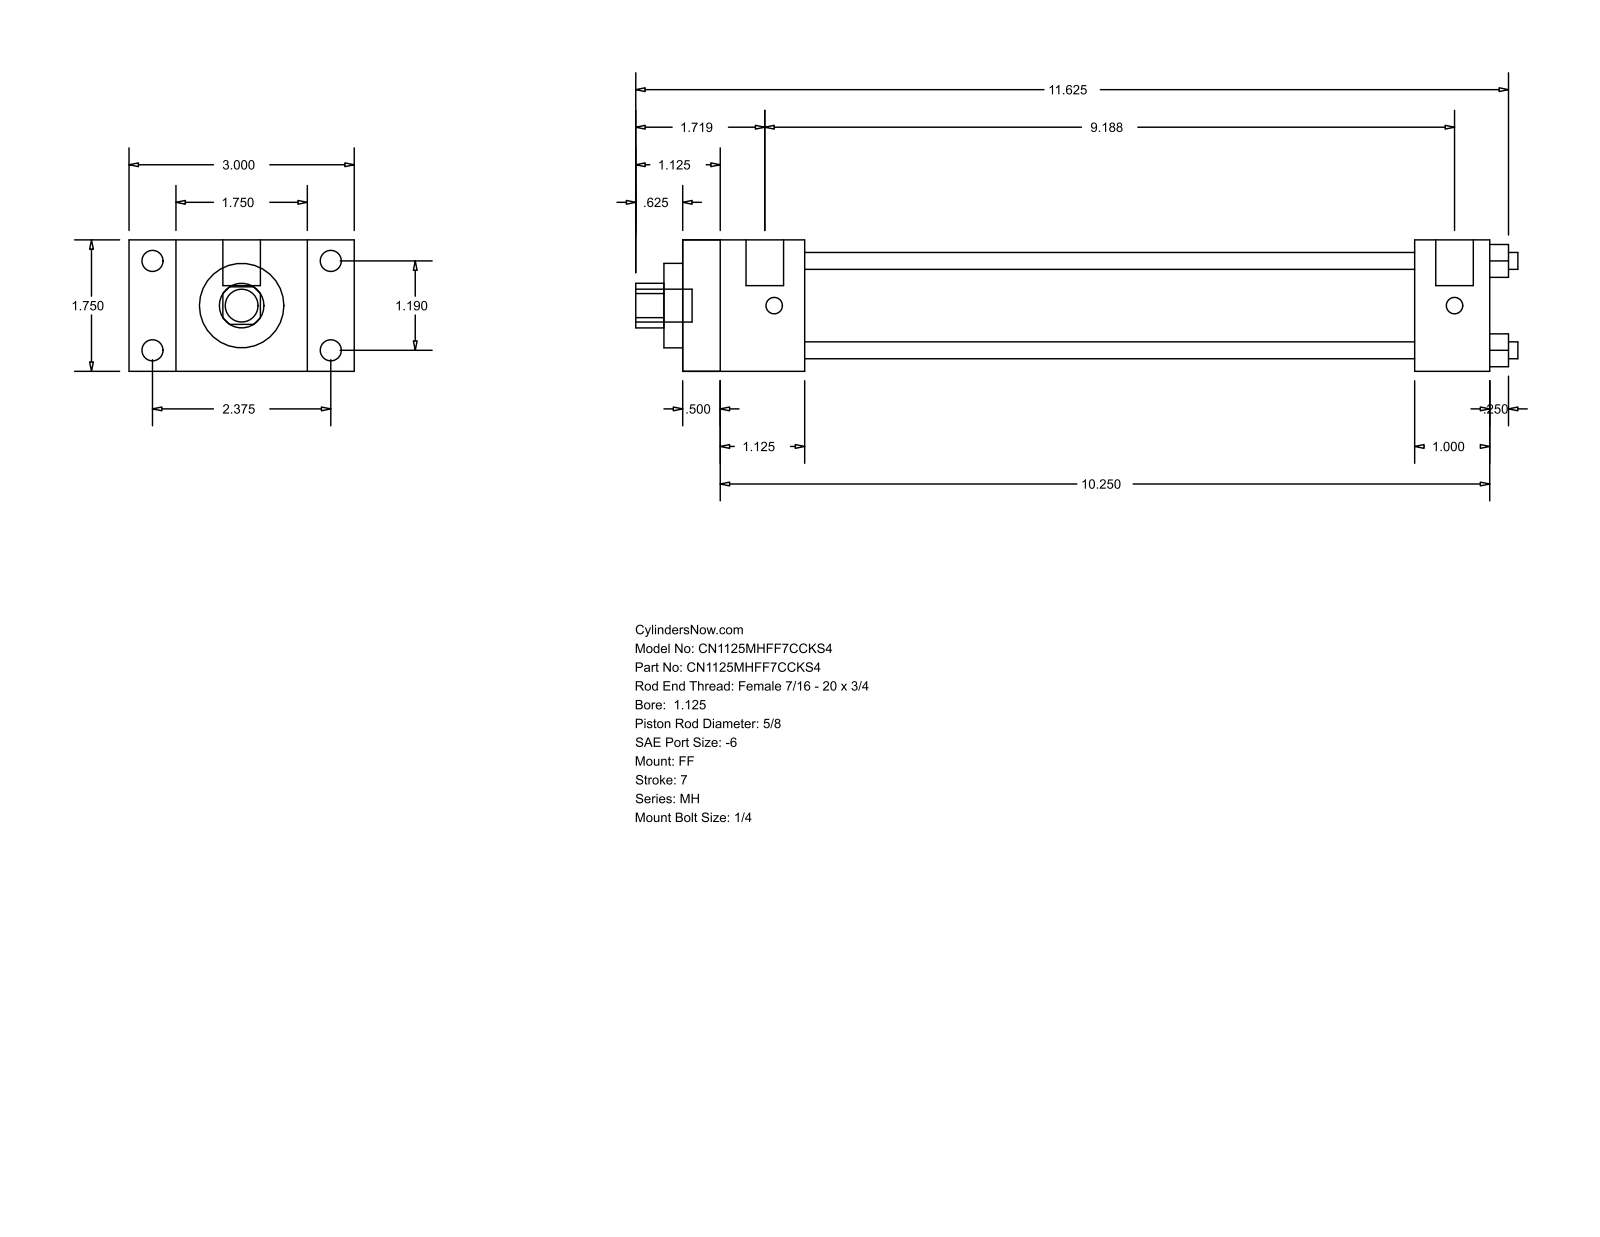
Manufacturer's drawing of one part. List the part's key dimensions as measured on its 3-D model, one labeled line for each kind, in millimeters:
Part name (STEP PRODUCT): MH_FF__0112_0.625
STEP written by: GSSL Pune (CONFIG_CONTROL_DESIGN)
Units: millimetres
Bodies: 0 solids, 92 faces (64 planar, 28 cylindrical, 0 other)
Overall size (bounding box): 298.45 × 76.2 × 44.45
Round holes (diameter × count): ⌀5.71 ×4, ⌀15.88 ×1, ⌀28.57 ×1, ⌀34.92 ×1
Round bosses / shafts (diameter × count): ⌀7.14 ×4, ⌀5.56 ×4, ⌀12.7 ×2, ⌀11.11 ×1
Partial cylindrical surfaces — rounded edges, fillets, slot ends (radius × count): R7.54 ×1
Main face-to-face distances: 44.46, 273.05, 12.69, 260.36, 15.87, 60.33, 28.58, 41.27, 247.64, 234.95
Hole centre spacings: 21.37, 30.22, 42.74
